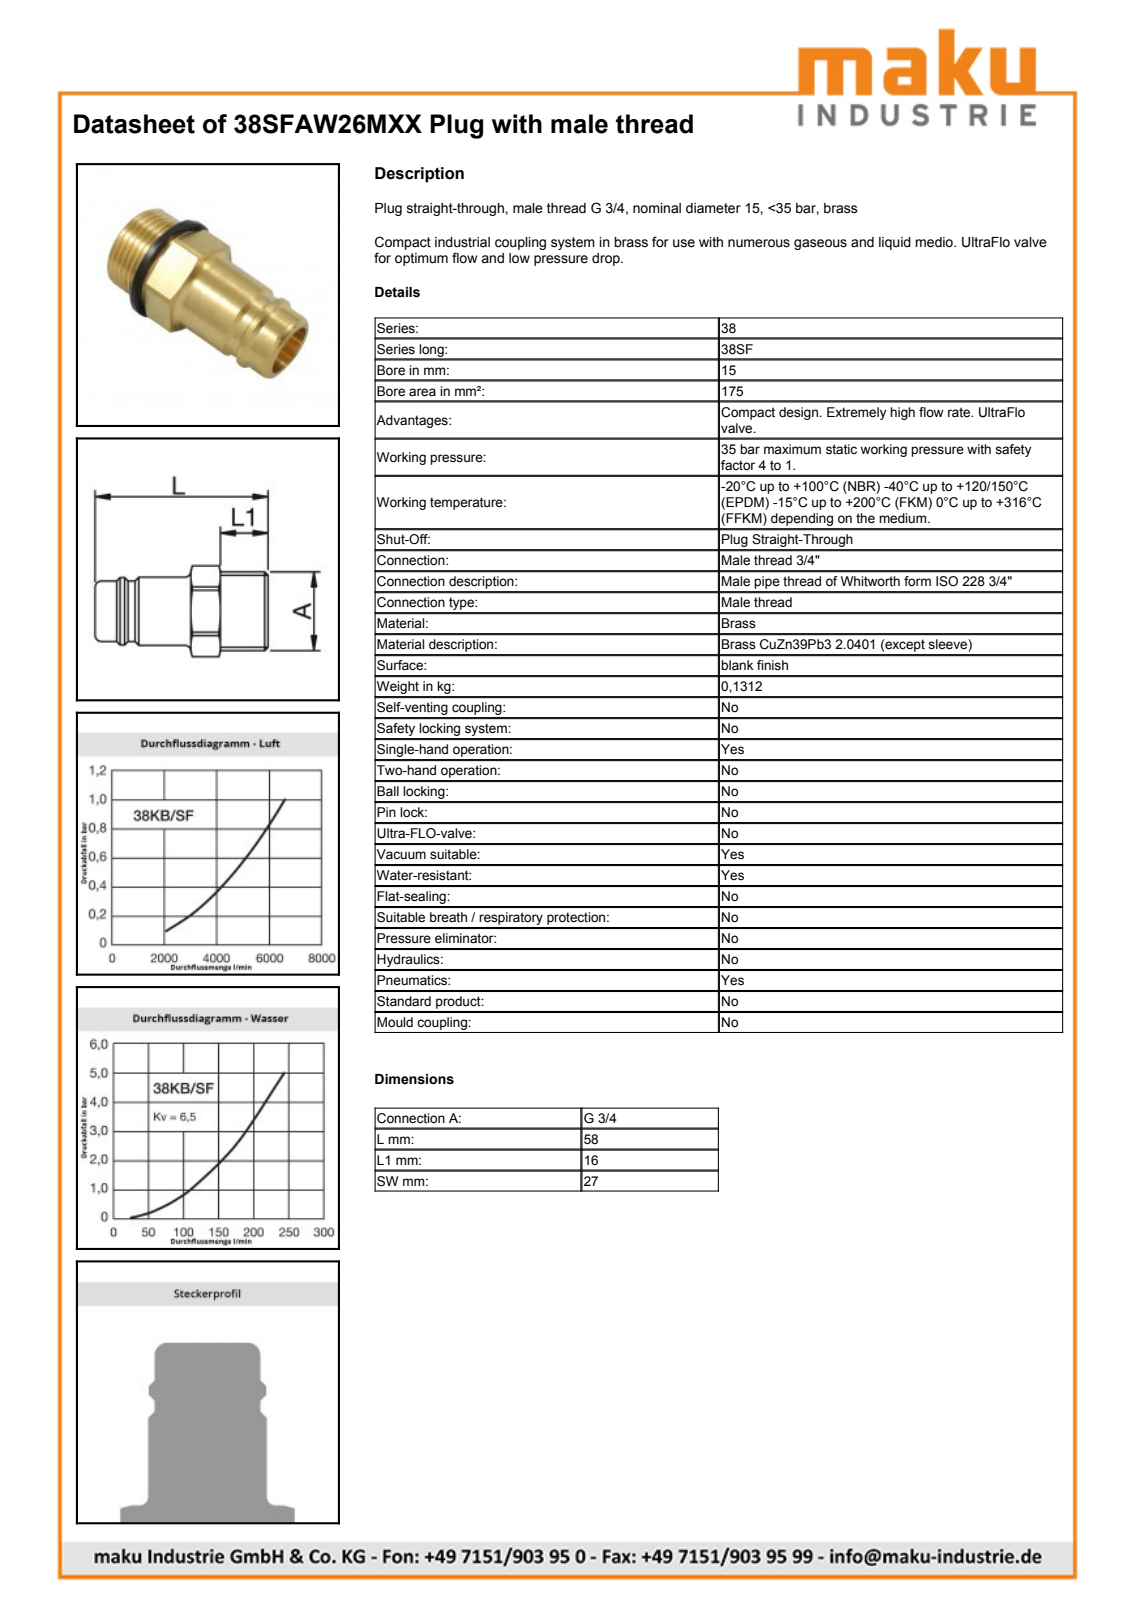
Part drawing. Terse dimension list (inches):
name: D107906; D107901; D103699
written by: Autodesk Inventor 2013 (AUTOMOTIVE_DESIGN)
unit: in
bodies: 2 solids, 50 faces (15 planar, 16 cylindrical, 19 other)
size: 2.283 × 1.26 × 1.26
volume: 1.032 in³; area: 13.49 in²
holes: 1× ⌀0.591
bosses: 1× ⌀1.26, 1× ⌀1.041, 1× ⌀0.9, 1× ⌀0.89, 1× ⌀0.799
rounds: 1× R0.524, 1× R0.599
face distances: 1.063, 0.079, 0.63, 0.551, 0.022, 1.041, 1.654, 1.732, 2.283, 1.264
